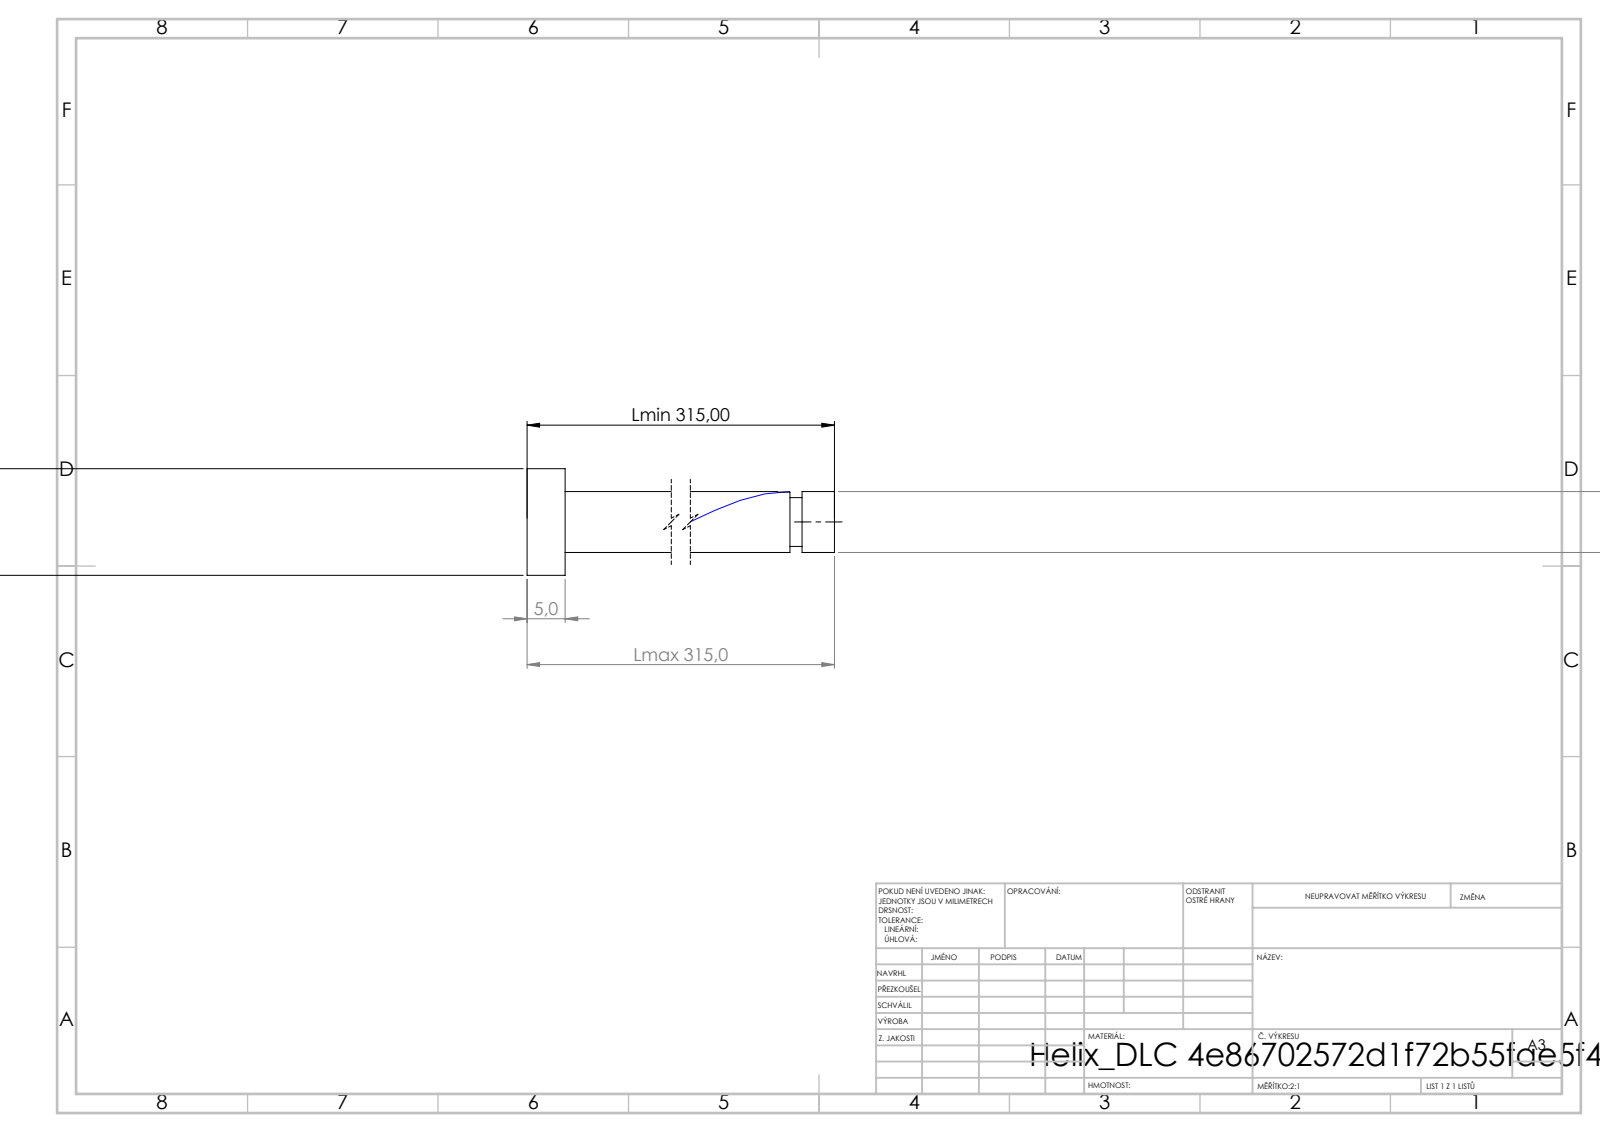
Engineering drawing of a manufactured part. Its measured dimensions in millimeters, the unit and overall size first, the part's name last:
Units: millimetres
Overall size (bounding box): 315 × 14 × 14
Round bosses / shafts (diameter × count): ⌀14 ×1, ⌀8 ×1, ⌀6.4 ×1
Main face-to-face distances: 5, 315, 310, 310.75, 305.75, 4.25, 309.15, 304.15, 1.6, 5.85
Volume: 16 171 mm³ · Surface area: 8 484 mm²
Bodies: 1 solid, 21 faces (6 planar, 14 cylindrical, 1 other)
STEP written by: SolidWorks 2019 (CONFIG_CONTROL_DESIGN)
